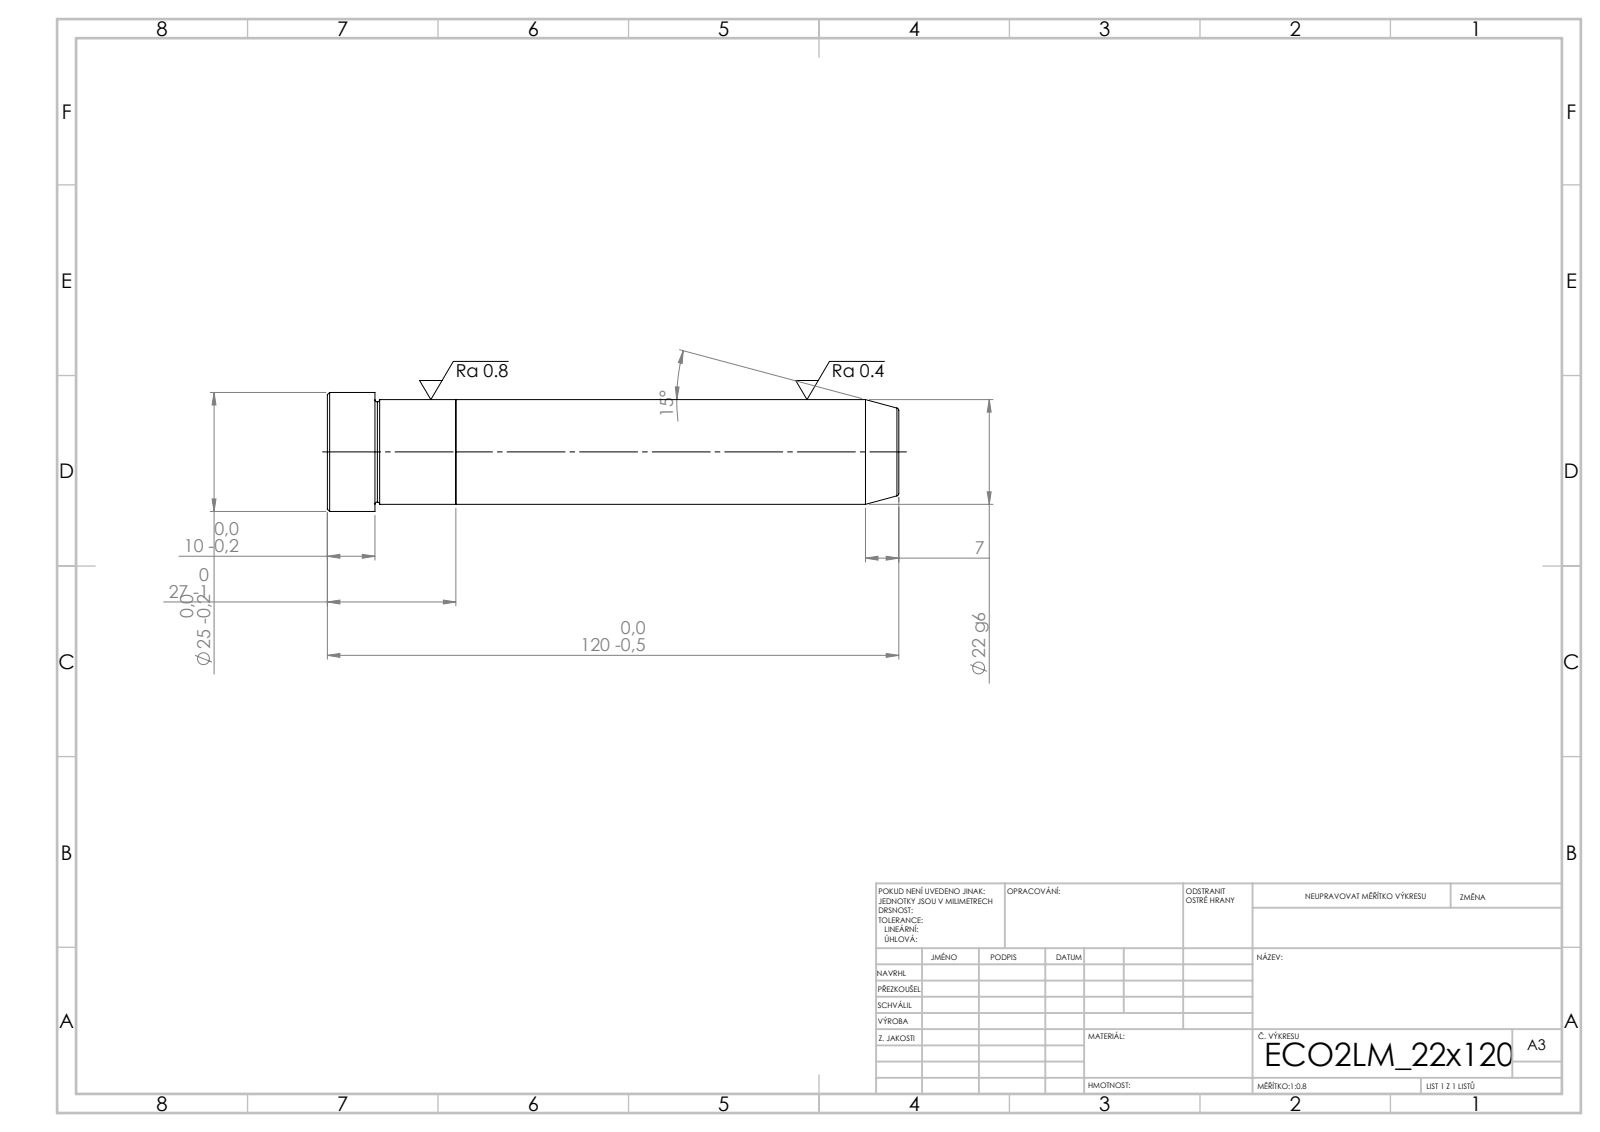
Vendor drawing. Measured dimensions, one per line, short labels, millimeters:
written by: SolidWorks 2019 (CONFIG_CONTROL_DESIGN)
unit: mm
bodies: 2 solids, 21 faces (5 planar, 6 cylindrical, 10 other)
size: 120 × 25 × 25
volume: 46 257 mm³; area: 9 992 mm²
bosses: 1× ⌀25, 1× ⌀22
face distances: 27, 93, 120, 110, 17, 10
